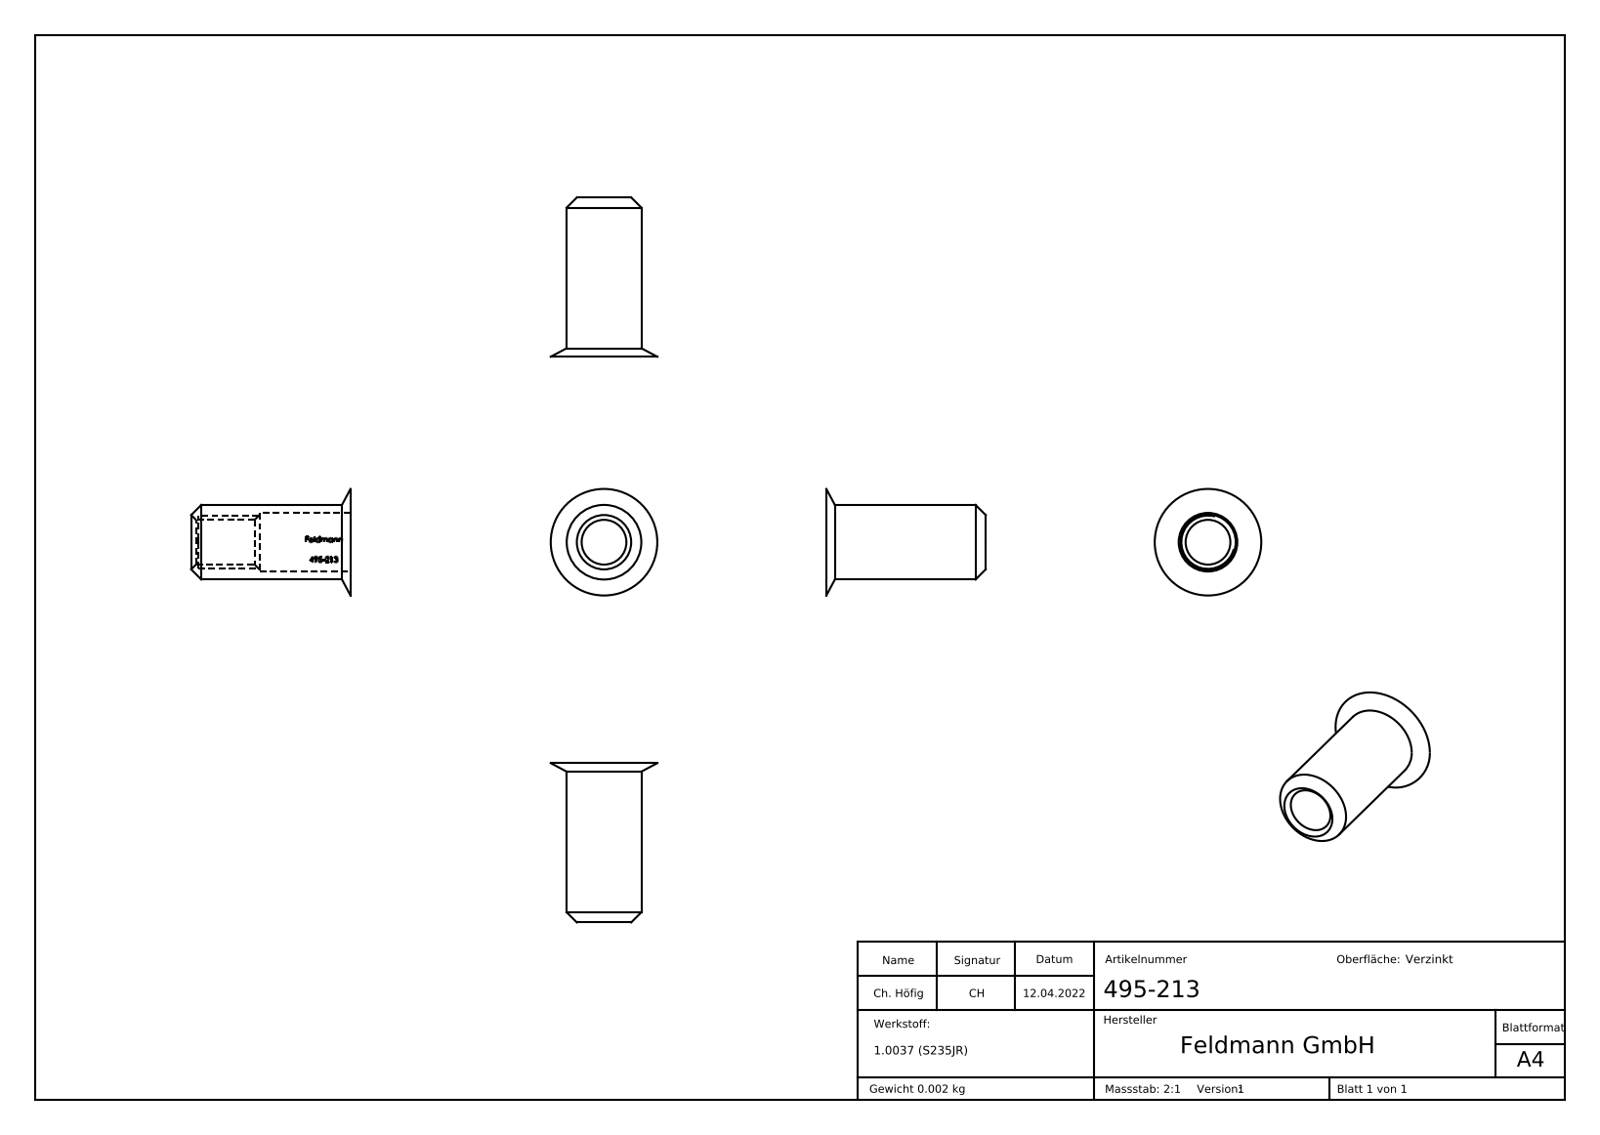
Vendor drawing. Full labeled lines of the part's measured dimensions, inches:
Part name (STEP PRODUCT): 495-213
STEP written by: SolidWorks 2018 (CONFIG_CONTROL_DESIGN)
Units: inches
Bodies: 1 solid, 210 faces (100 planar, 29 cylindrical, 81 other)
Overall size (bounding box): 0.589 × 0.394 × 0.394
Volume: 0.018 in³ · Surface area: 1.02 in²
Round holes (diameter × count): ⌀0.165 ×1, ⌀0.217 ×1
Round bosses / shafts (diameter × count): ⌀0.276 ×1
Partial cylindrical surfaces — rounded edges, fillets, slot ends (radius × count): R0.112 ×1
Main face-to-face distances: 0.335, 0.072, 0.026, 0.053, 0.074, 0.069, 0.047, 0.07, 0.066, 0.07
